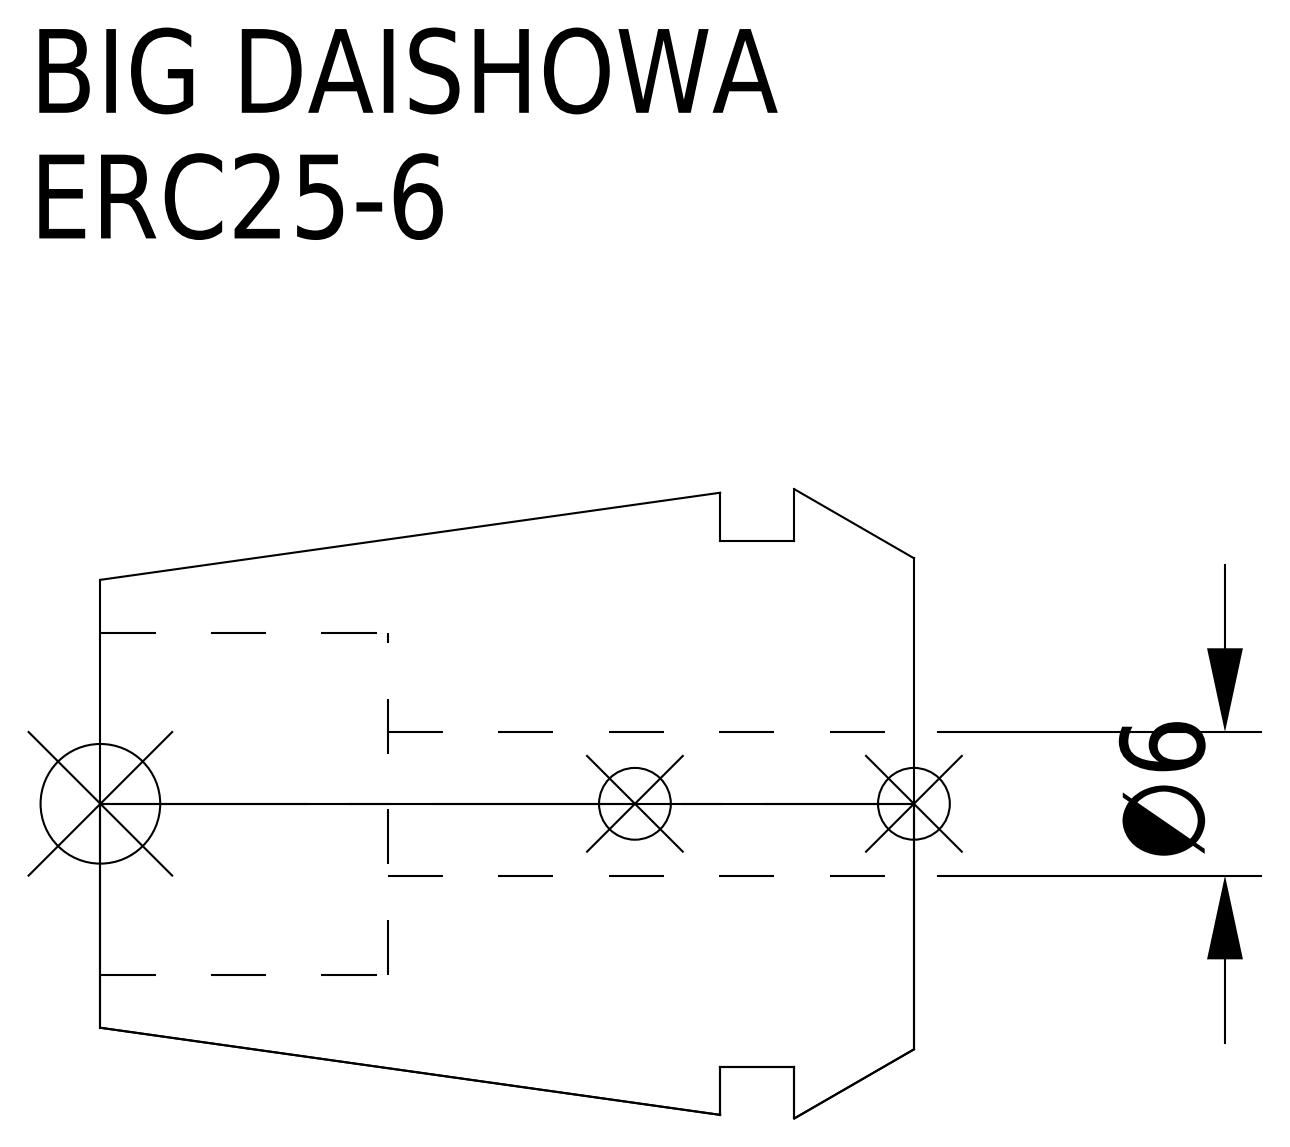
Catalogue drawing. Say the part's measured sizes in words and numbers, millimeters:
The part is named "ERC25-6". Its 3-D file was written by "CREO PARAMETRIC BY PTC INC, 2016380 (AUTOMOTIVE_DESIGN)". It is 1 solid with 15 faces: 5 planar, 6 cylindrical and 4 other. Overall it measures 34 by 26.3 by 26.3 millimeters. Its volume is 11 053 cubic millimeters and its surface area 4 294 square millimeters. Round holes: 1 of diameter 6, 1 of diameter 14.3. Round bosses or shafts: 1 of diameter 22. The main face-to-face distances are 5, 8.1, 3.1, 22, 17, 13.9, 34, 29, 25.9, 12.
